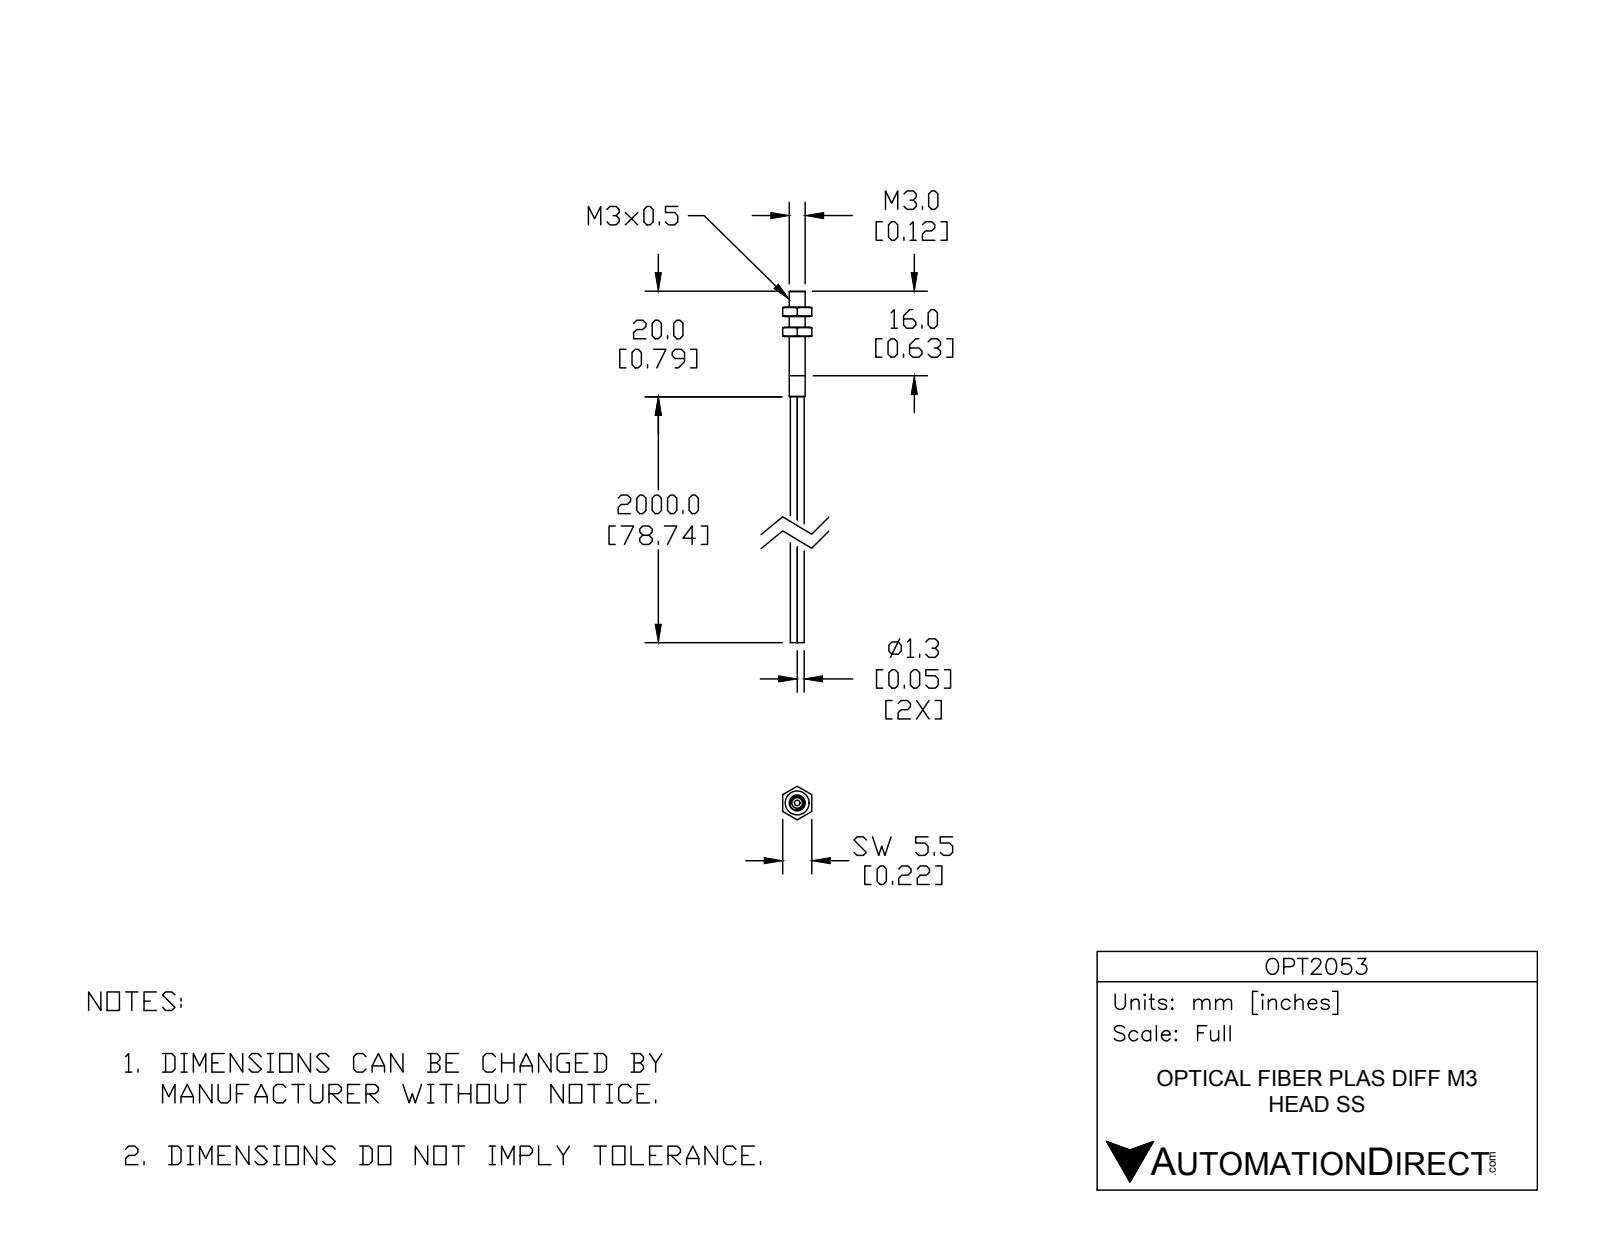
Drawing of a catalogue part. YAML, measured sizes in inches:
part_name: "OPT2053"
step_written_by: "SolidWorks 2014 (AUTOMOTIVE_DESIGN)"
units: inches
bodies: {solids: 1, faces: 40, planar: 19, cylindrical: 9, other: 12}
overall_size: [2.618, 0.25, 0.217]
volume: 0.02
surface_area: 1.054
round_bosses_or_shafts:
  - {diameter: 0.051, count: 2}
  - {diameter: 0.118, count: 1}
face_to_face_distances: [0.217, 0.071, 0.15, 0.22, 0.079, 0.339, 0.268, 0.189, 0.118, 0.449]
